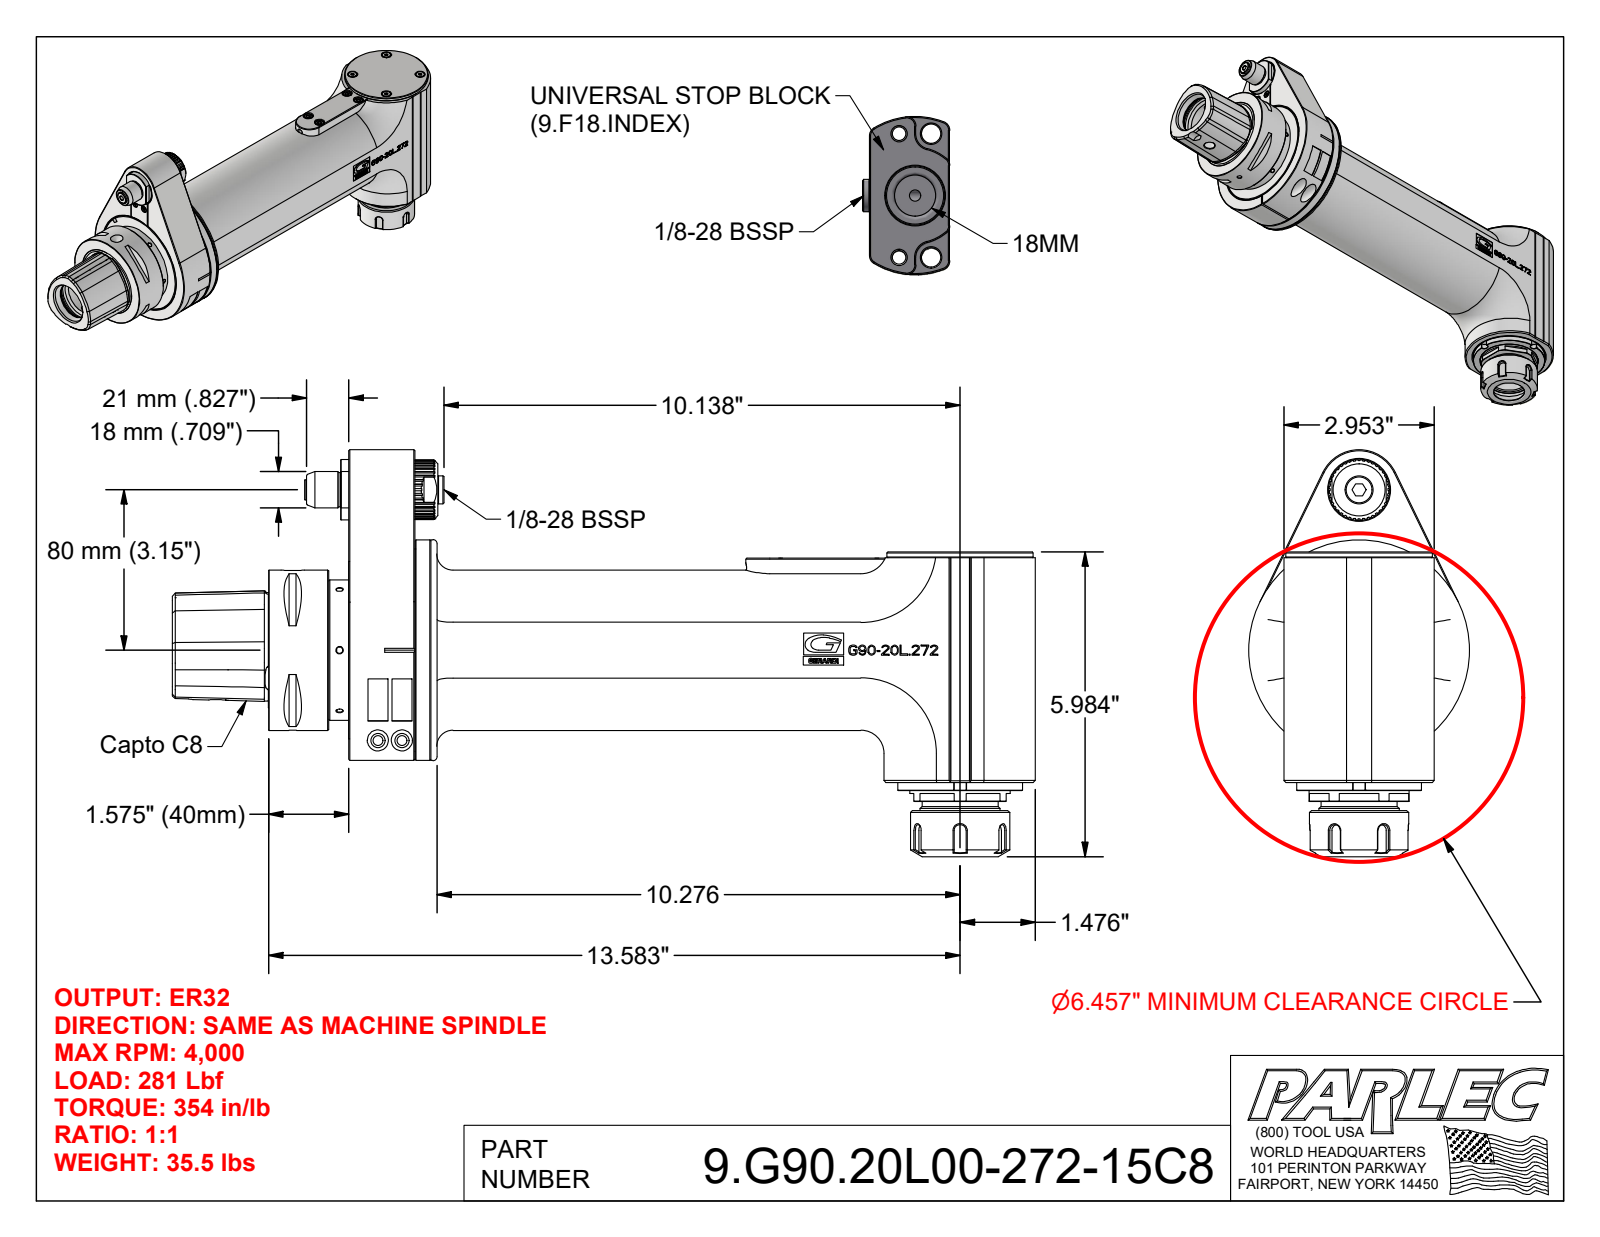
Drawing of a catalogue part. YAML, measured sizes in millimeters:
part_name: "9.G90.20L00-272-15C8"
step_written_by: "Autodesk Inventor 2022 (AUTOMOTIVE_DESIGN)"
units: millimeters
bodies: {solids: 3, faces: 1676, planar: 959, cylindrical: 264, other: 453}
overall_size: [430.5, 203, 110]
volume: 1604000
surface_area: 325900
round_holes:
  - {diameter: 5, count: 12}
  - {diameter: 3.3, count: 6}
  - {diameter: 4.2, count: 5}
  - {diameter: 8, count: 4}
  - {diameter: 4, count: 3}
  - {diameter: 8.5, count: 3}
  - {diameter: 3, count: 2}
  - {diameter: 6, count: 2}
  - {diameter: 7, count: 2}
  - {diameter: 9.2, count: 2}
  - {diameter: 10.5, count: 2}
  - {diameter: 11, count: 2}
round_bosses_or_shafts:
  - {diameter: 7, count: 5}
  - {diameter: 7.8, count: 4}
  - {diameter: 35, count: 2}
  - {diameter: 12.8, count: 2}
  - {diameter: 9, count: 2}
  - {diameter: 5.8, count: 2}
  - {diameter: 110, count: 1}
  - {diameter: 102, count: 1}
partial_cylinders:
  - {radius: 3, count: 11}
  - {radius: 2.2, count: 2}
  - {radius: 5.7, count: 2}
  - {radius: 8, count: 2}
  - {radius: 11.9, count: 2}
  - {radius: 12, count: 2}
  - {radius: 40, count: 2}
  - {radius: 2, count: 1}
face_to_face_distances: [75, 3, 33, 33.1, 2, 2.9, 48, 36, 0.5, 10]
hole_center_spacings: [47.5, 82.3, 47.5, 95, 13, 5.1, 8.9, 13.7]
